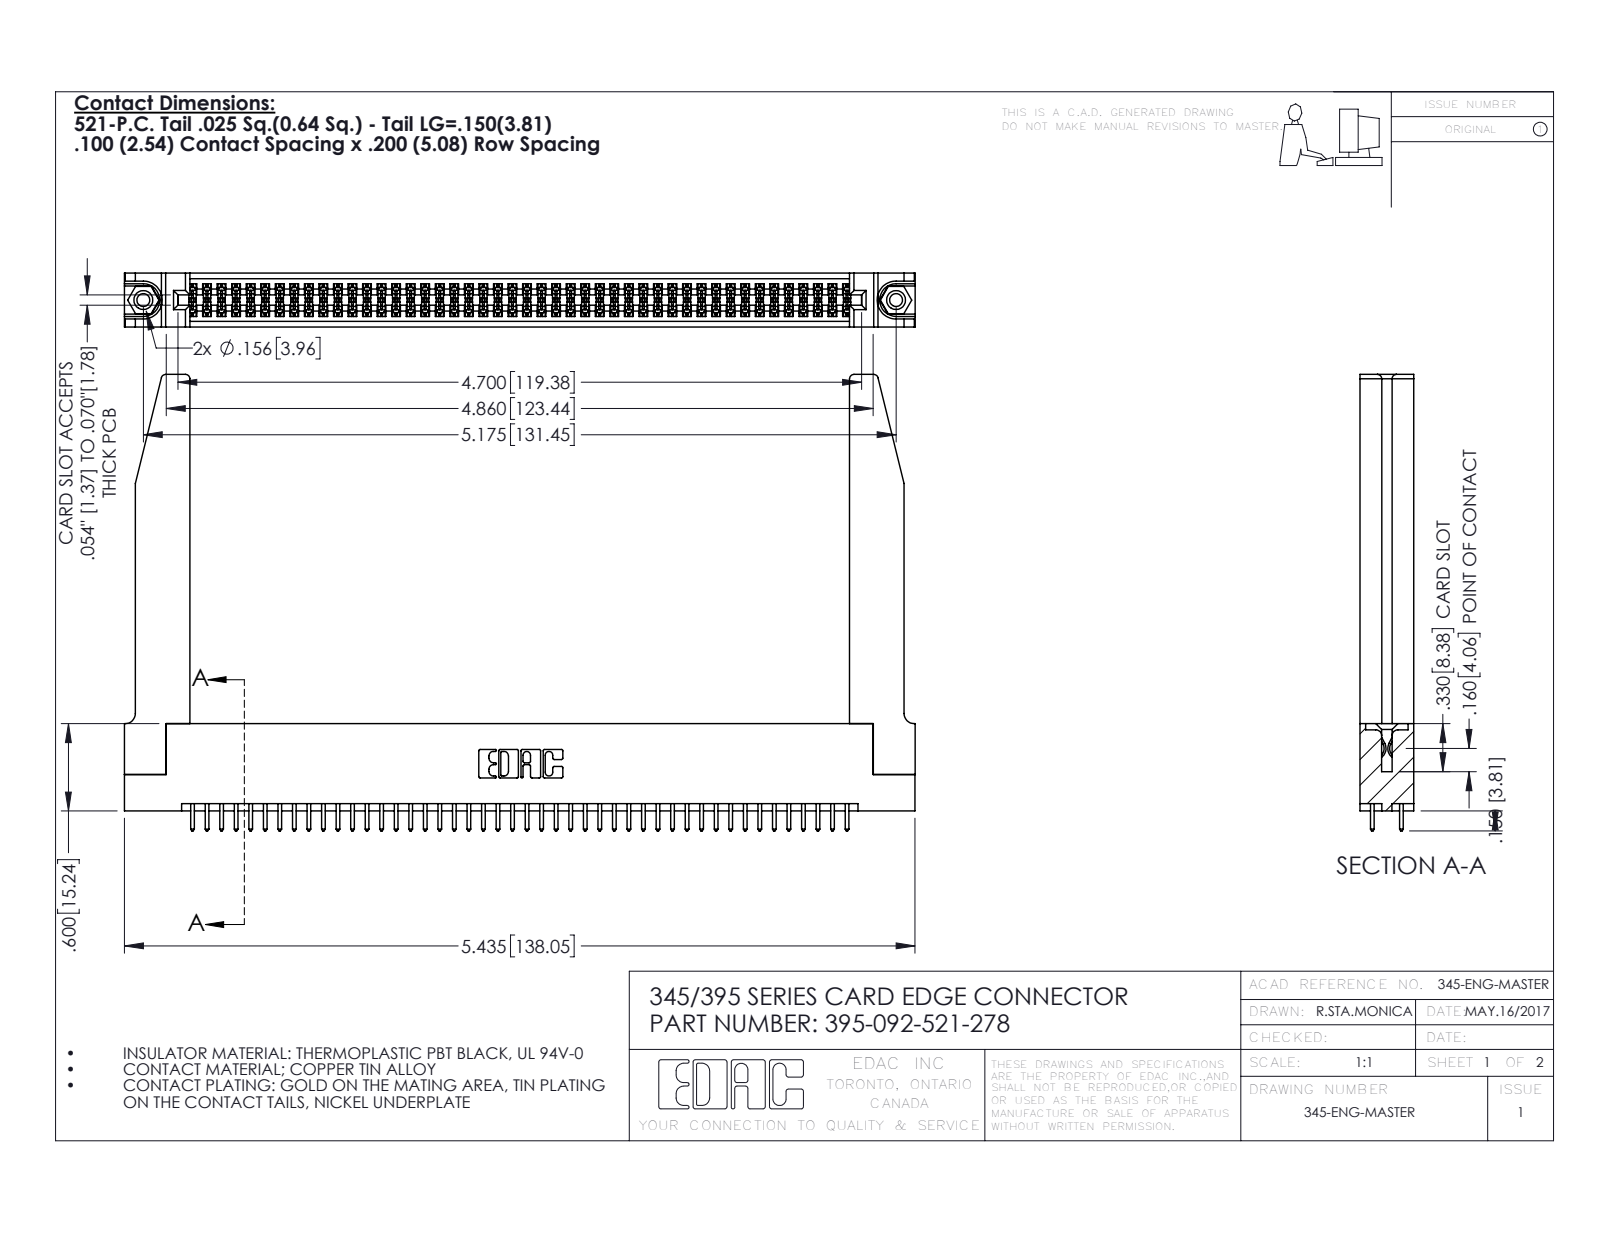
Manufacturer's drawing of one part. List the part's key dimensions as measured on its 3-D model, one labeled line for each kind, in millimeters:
Part name (STEP PRODUCT): 395-092-521-278; 345-220-078_345-220-078; 345-250-001_345-250-001-102; 345 Part_Flush Mounting Lugs - 0.156 Dia-TH (+1 more)
STEP written by: SolidWorks 2016 (CONFIG_CONTROL_DESIGN)
Units: millimetres
Bodies: 97 solids, 4960 faces (3258 planar, 1650 cylindrical, 52 other)
Overall size (bounding box): 138.1 × 79.7 × 9.4
Volume: 21 190 mm³ · Surface area: 26 500 mm²
Round holes (diameter × count): ⌀2.3 ×2, ⌀3.2 ×2, ⌀4 ×2, ⌀1.6 ×1
Round bosses / shafts (diameter × count): ⌀3.9 ×2
Partial cylindrical surfaces — rounded edges, fillets, slot ends (radius × count): R0.2 ×138, R0.3 ×92, R0.3 ×22, R0.8 ×8, R0.2 ×6, R0.8 ×6, R0.7 ×3, R0.4 ×2
Main face-to-face distances: 1.8, 9.4, 7.6, 5.1, 2.5, 6.9, 0.6, 5.7, 4.4, 3.8
Hole centre spacings: 6.9, 125.5, 131.4
